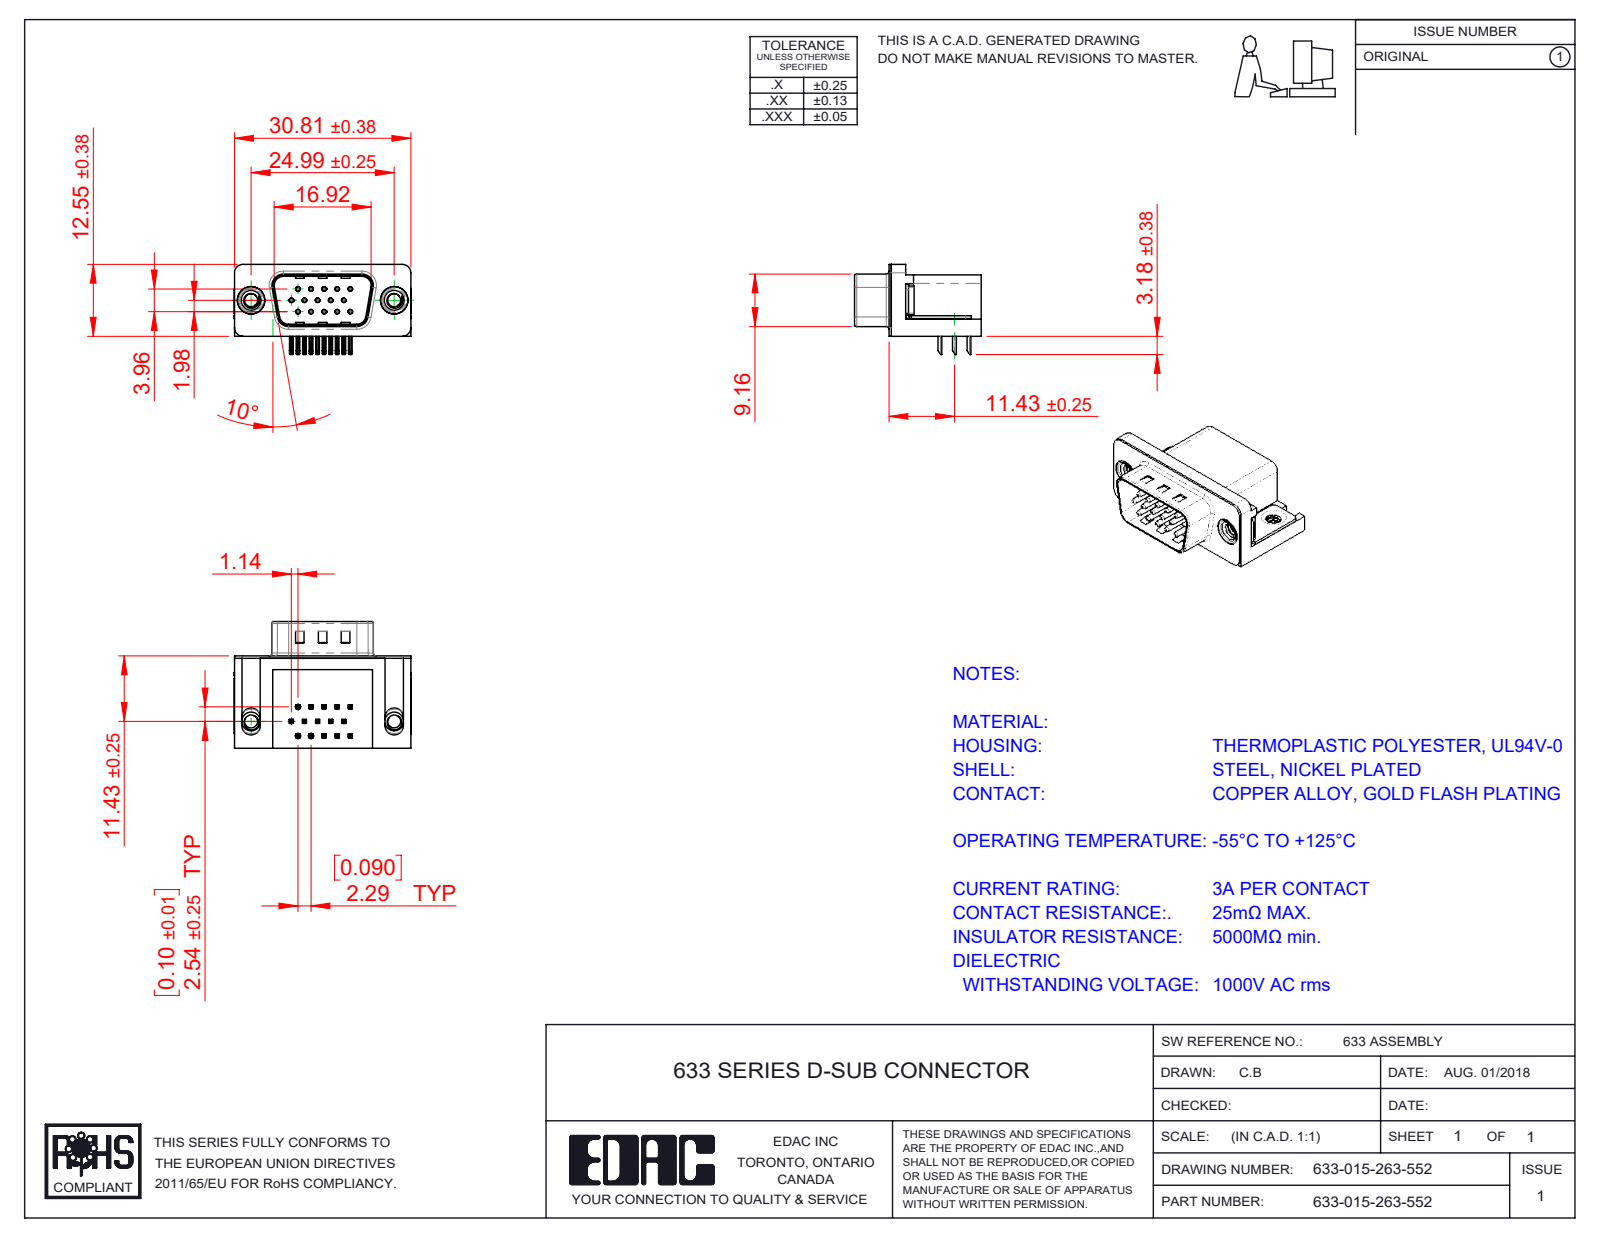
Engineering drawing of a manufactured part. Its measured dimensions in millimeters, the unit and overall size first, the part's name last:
Units: millimetres
Overall size (bounding box): 30.89 × 22.1 × 16.25
Round holes (diameter × count): ⌀0.35 ×15, ⌀0.8 ×15, ⌀2 ×2, ⌀2.26 ×2, ⌀4 ×2, ⌀4.8 ×2, ⌀5 ×2
Round bosses / shafts (diameter × count): ⌀0.75 ×15, ⌀4.9 ×2, ⌀4.75 ×2, ⌀3.9 ×2, ⌀3 ×2
Partial cylindrical surfaces — rounded edges, fillets, slot ends (radius × count): R0.25 ×72, R0.12 ×30, R1 ×16, R0.5 ×9, R1.6 ×8, R1.5 ×7, R0.9 ×4, R2 ×4
Main face-to-face distances: 0.4, 10.35, 15.7, 2.9, 6.7, 16.1, 2.5, 0.5, 0.35, 10.7
Hole centre spacings: 3.96, 2.28, 4.57, 2.29, 6.05, 6.86, 7.92, 6.04
Volume: 4 084 mm³ · Surface area: 5 499 mm²
Bodies: 21 solids, 1563 faces (903 planar, 449 cylindrical, 211 other)
Part name (STEP PRODUCT): 633 Contact Bottom; 633 Shell_15 Contact; 633 4 Prong Board Lock; 633 Housing_15 Contact (+4 more)
STEP written by: SolidWorks 2016 (CONFIG_CONTROL_DESIGN)
